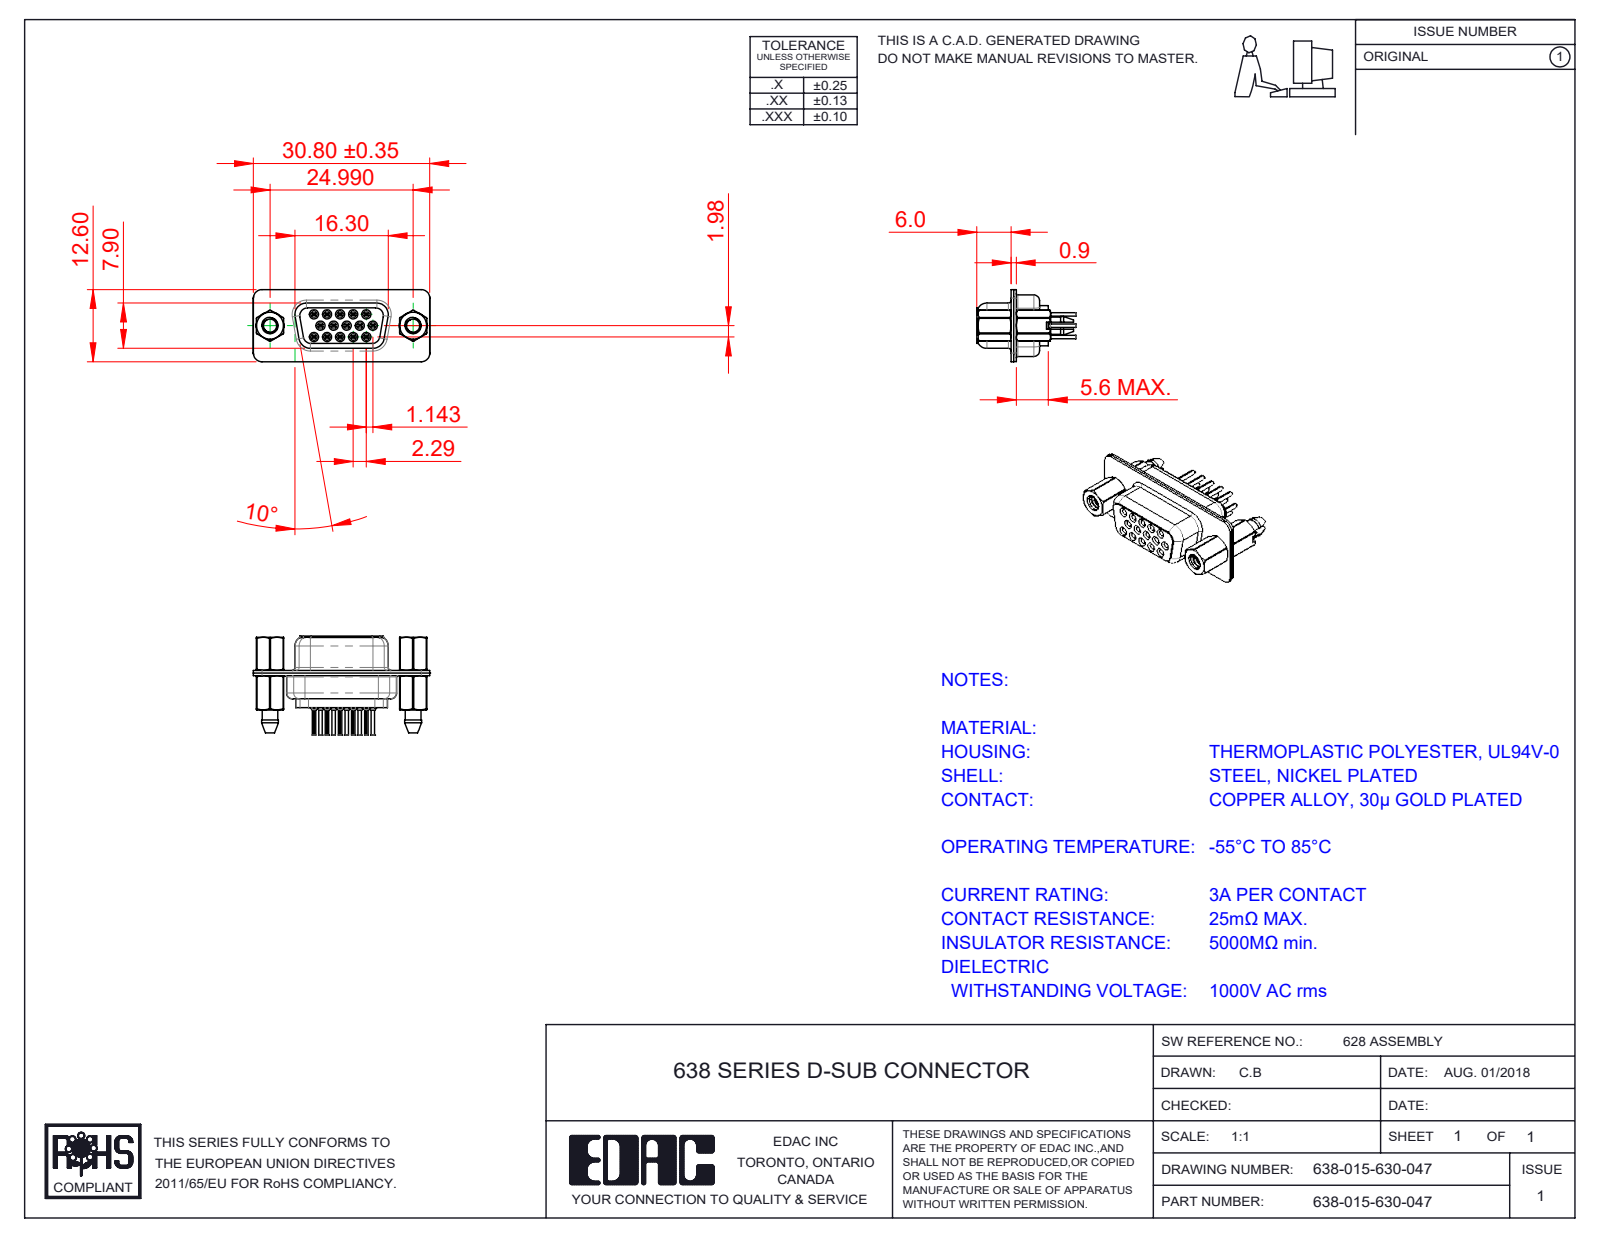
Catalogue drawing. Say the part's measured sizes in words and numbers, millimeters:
The part is named "638 Shell Front_15 Contacts; 638 Housing_15 Contacts; 638 Contact Row 1_30; 638 Shell Rear_15 Contacts (+5 more)". Its 3-D file was written by "SolidWorks 2020 (CONFIG_CONTROL_DESIGN)". It is 22 solids with 2384 faces: 586 planar, 736 cylindrical and 1062 other. Overall it measures 30.81 by 17.3 by 12.6 millimeters. Its volume is 1 901 cubic millimeters and its surface area 6 366 square millimeters. Round holes: 15 of diameter 0.2, 15 of diameter 0.8, 15 of diameter 1, 15 of diameter 1.1, 15 of diameter 1.6, 15 of diameter 1.7, 15 of diameter 1.8, 2 of diameter 2, 2 of diameter 2.26, 2 of diameter 2.29, 2 of diameter 4, 2 of diameter 4.05. Round bosses or shafts: 15 of diameter 2, 15 of diameter 1.5, 15 of diameter 1.2, 15 of diameter 0.6, 2 of diameter 4.95, 2 of diameter 4.8, 2 of diameter 2.79. Partial cylindrical surfaces (rounded edges, fillets, slot ends): 30 of radius 0.1, 22 of radius 1.5, 12 of radius 2, 10 of radius 0.28, 8 of radius 1.55, 5 of radius 1.35, 4 of radius 0.25, 4 of radius 0.5. The main face-to-face distances are 0.45, 0.9, 0.4, 1.43, 8.88, 4.76, 6.6, 1.4, 12.5, 2.28. The hole center spacings are 3.96, 2.28, 4.57, 2.29, 6.05, 6.04, 6.86, 7.92.
